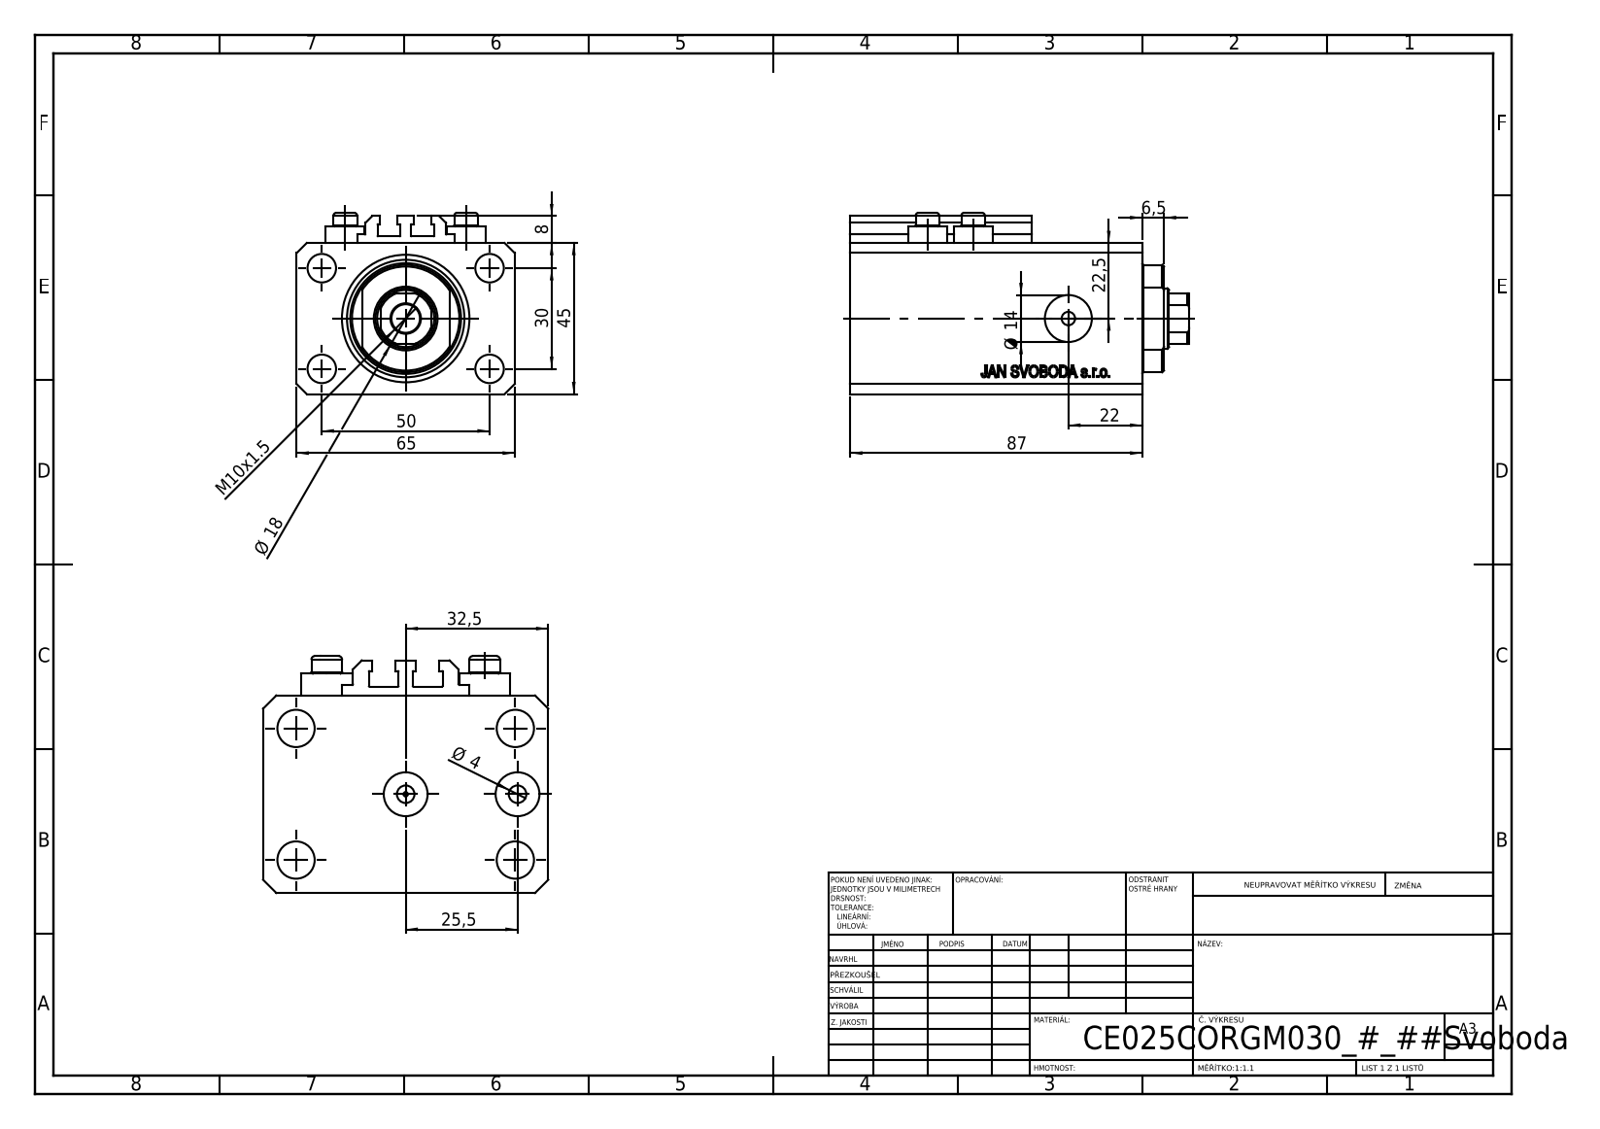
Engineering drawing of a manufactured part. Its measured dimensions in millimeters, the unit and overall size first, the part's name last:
Units: millimetres
Overall size (bounding box): 101 × 65 × 54
Round holes (diameter × count): ⌀4 ×8, ⌀8.5 ×5, ⌀10 ×2, ⌀14 ×2, ⌀1.25 ×1, ⌀18 ×1, ⌀25 ×1, ⌀38 ×1
Round bosses / shafts (diameter × count): ⌀11.6 ×4, ⌀7 ×4
Partial cylindrical surfaces — rounded edges, fillets, slot ends (radius × count): R0.2 ×10, R8.5 ×1, R16 ×1
Main face-to-face distances: 45, 65, 14, 87, 73, 47, 6.9, 66.1, 80.1, 3
Hole centre spacings: 29.15, 13.6, 15.01, 30, 36, 38.48, 50, 52.68
Volume: 237 199 mm³ · Surface area: 63 237 mm²
Bodies: 8 solids, 1042 faces (504 planar, 92 cylindrical, 446 other)
Part name (STEP PRODUCT): ALLEN BOLT V250CE; V250CE_C_VCP; V250CE_C_Body; V250CE_VC_C
STEP written by: SolidWorks 2019 (CONFIG_CONTROL_DESIGN)
